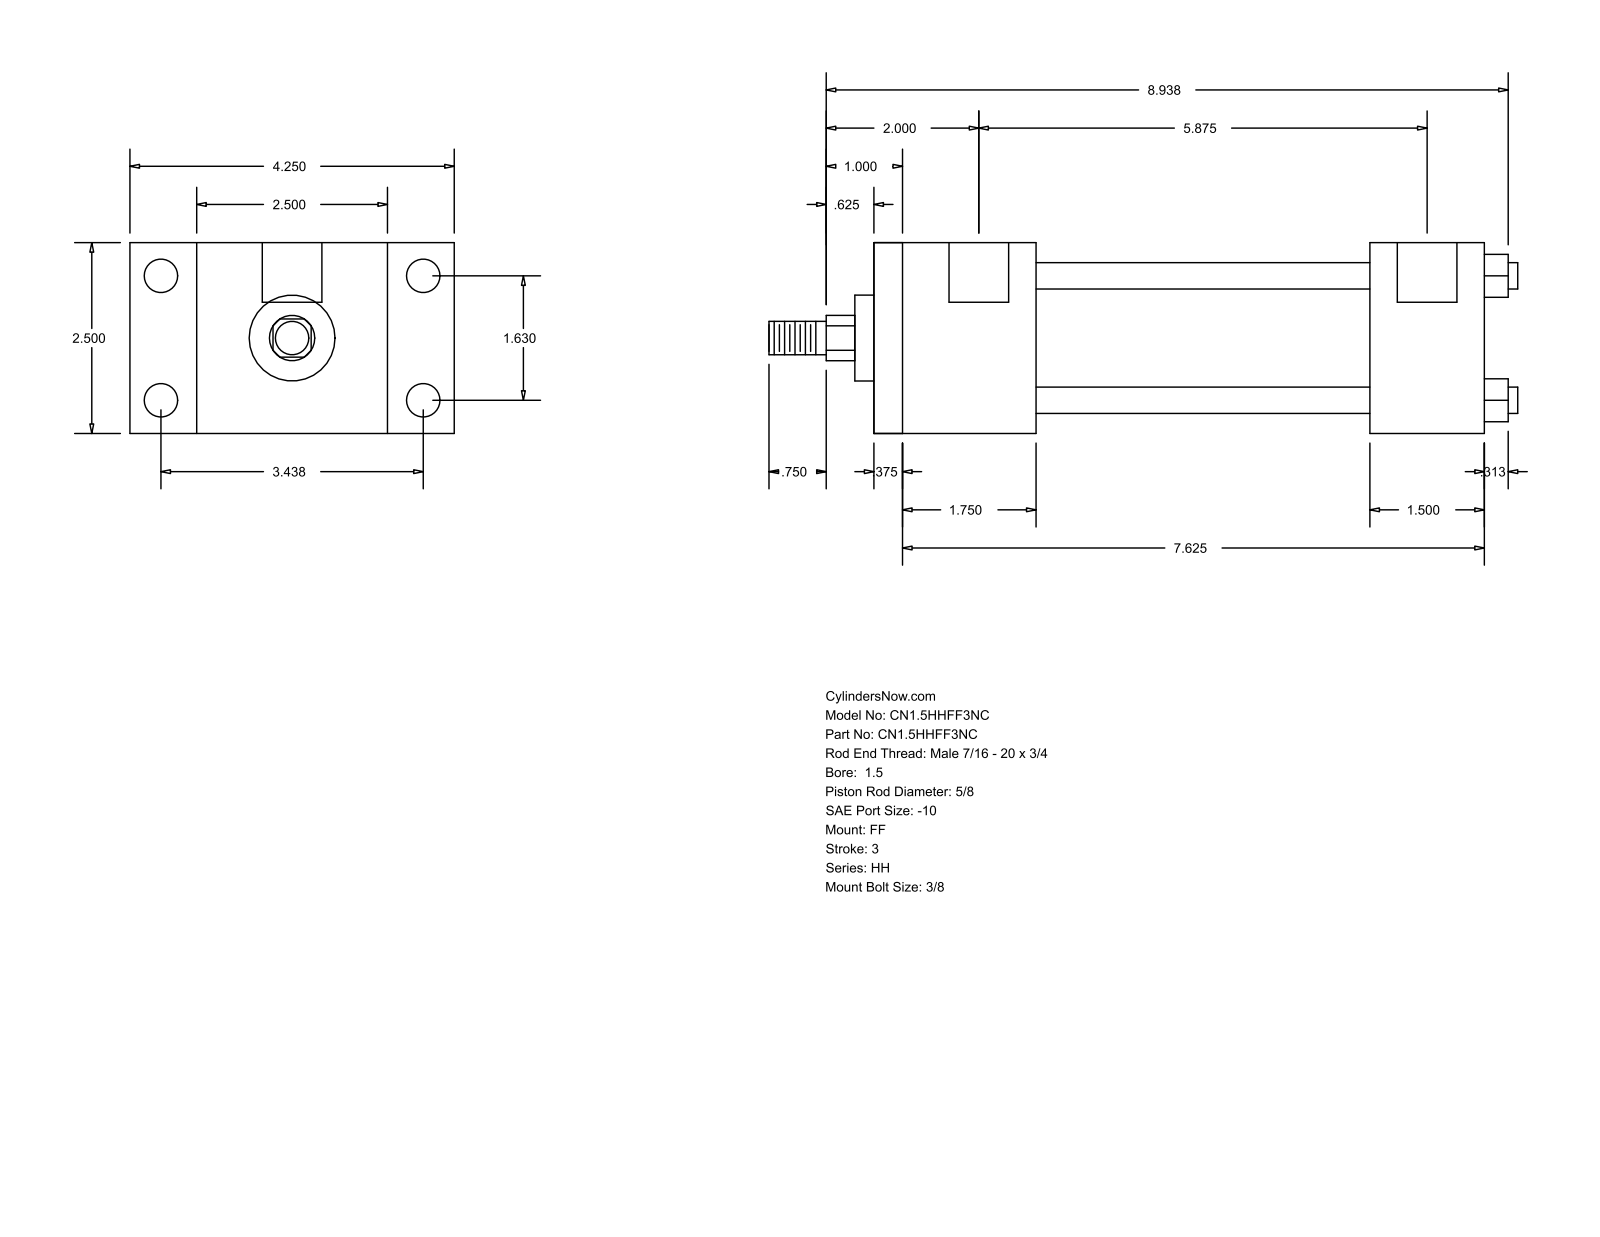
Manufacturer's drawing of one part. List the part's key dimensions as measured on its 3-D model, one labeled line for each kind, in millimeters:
Part name (STEP PRODUCT): HH_FF__0150_0.625
STEP written by: GSSL Pune (CONFIG_CONTROL_DESIGN)
Units: millimetres
Bodies: 0 solids, 92 faces (64 planar, 28 cylindrical, 0 other)
Overall size (bounding box): 249.24 × 107.95 × 63.5
Round holes (diameter × count): ⌀5.56 ×4, ⌀11.13 ×4, ⌀19.84 ×2
Round bosses / shafts (diameter × count): ⌀8.76 ×4, ⌀44.45 ×1, ⌀28.57 ×1, ⌀15.88 ×1, ⌀11.11 ×1
Partial cylindrical surfaces — rounded edges, fillets, slot ends (radius × count): R7.54 ×1
Main face-to-face distances: 63.5, 203.19, 38.1, 9.52, 193.67, 44.45, 53.97, 149.22, 165.09, 155.57
Hole centre spacings: 41.4, 87.32, 96.64, 152.4, 1.58, 1.59, 149.23, 150.81
